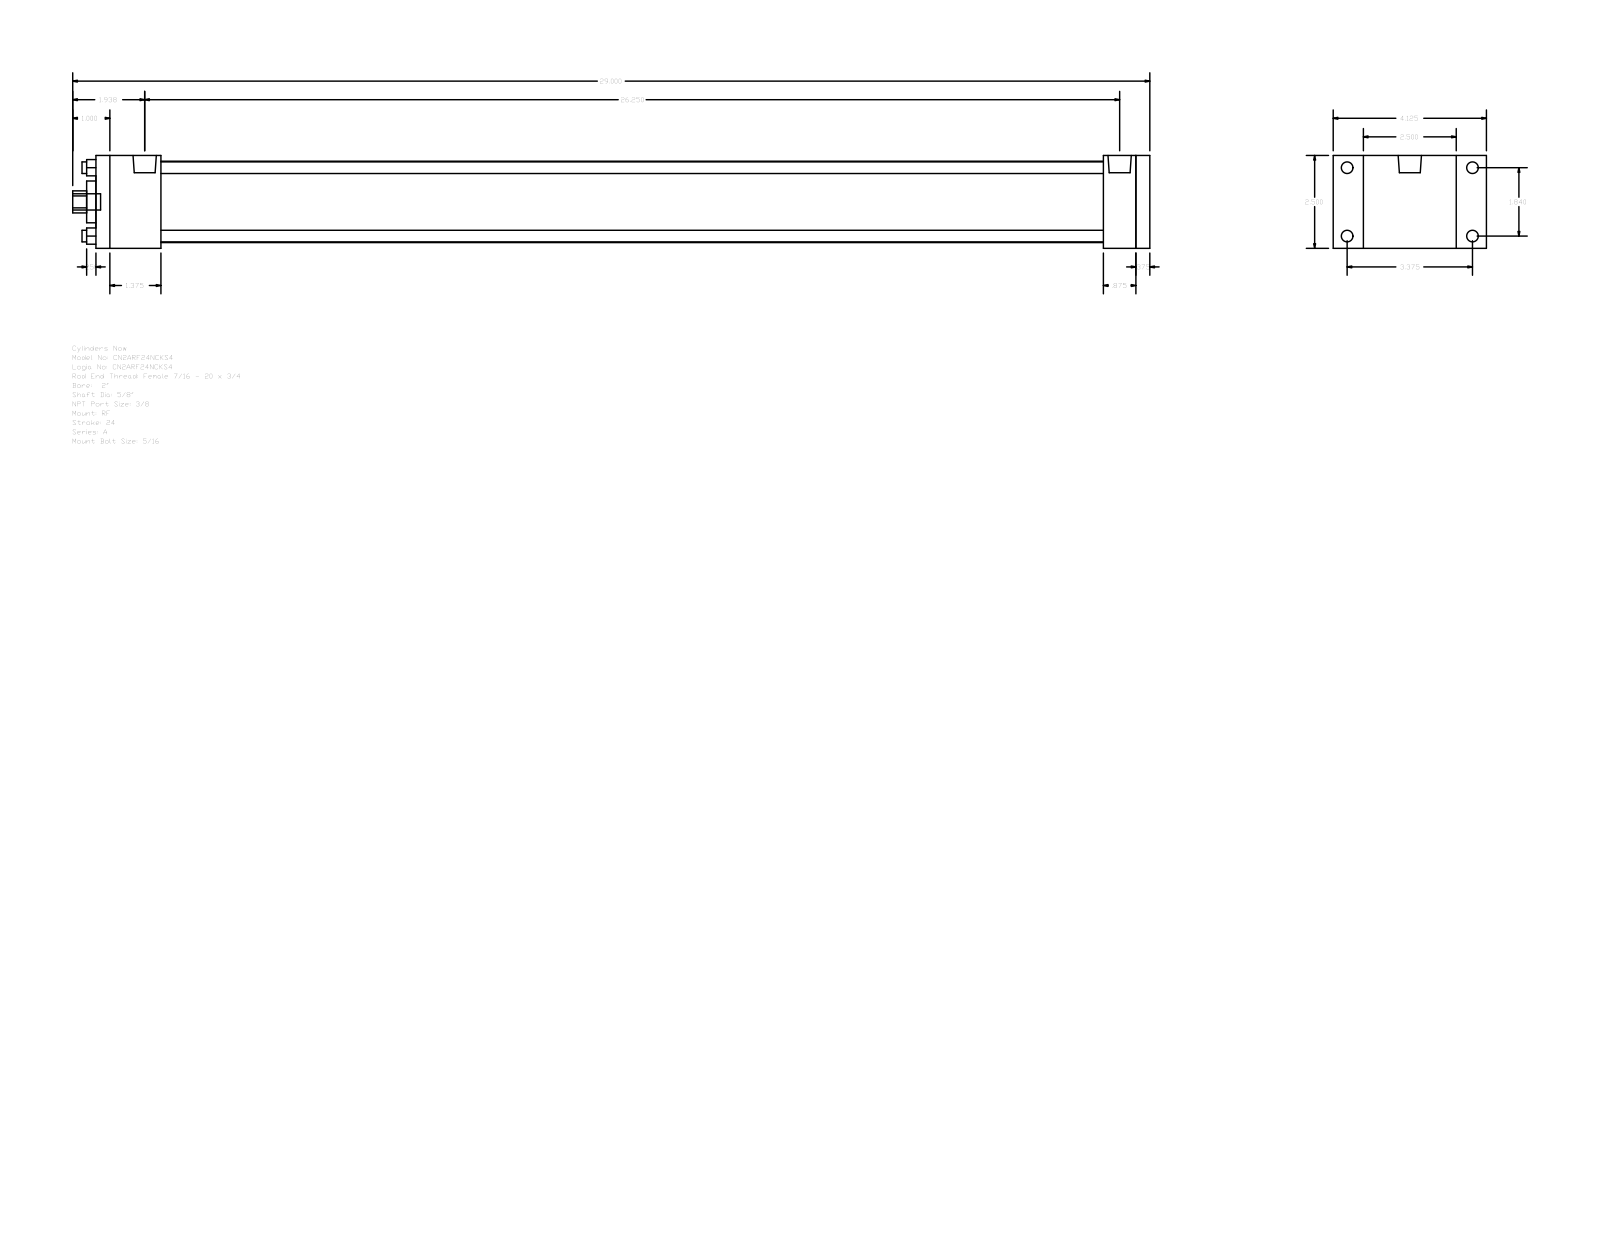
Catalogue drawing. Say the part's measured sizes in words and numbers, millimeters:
The part is named "A_RF__0200_0.625". Its 3-D file was written by "GSSL Pune (CONFIG_CONTROL_DESIGN)". It is 0 solids with 92 faces: 64 planar, 28 cylindrical and 0 other. Overall it measures 736.6 by 104.78 by 63.5 millimeters. Round holes: 4 of diameter 7.94, 1 of diameter 15.88, 1 of diameter 28.57, 1 of diameter 55.63. Round bosses or shafts: 4 of diameter 7.94, 4 of diameter 5.56, 2 of diameter 15.93, 1 of diameter 11.11. Partial cylindrical surfaces (rounded edges, fillets, slot ends): 1 of radius 7.54. The main face-to-face distances are 63.5, 720.72, 9.52, 711.2, 44.45, 666.75, 676.27, 688.97, 644.52, 22.23. The hole center spacings are 33.05, 46.74, 66.1.
